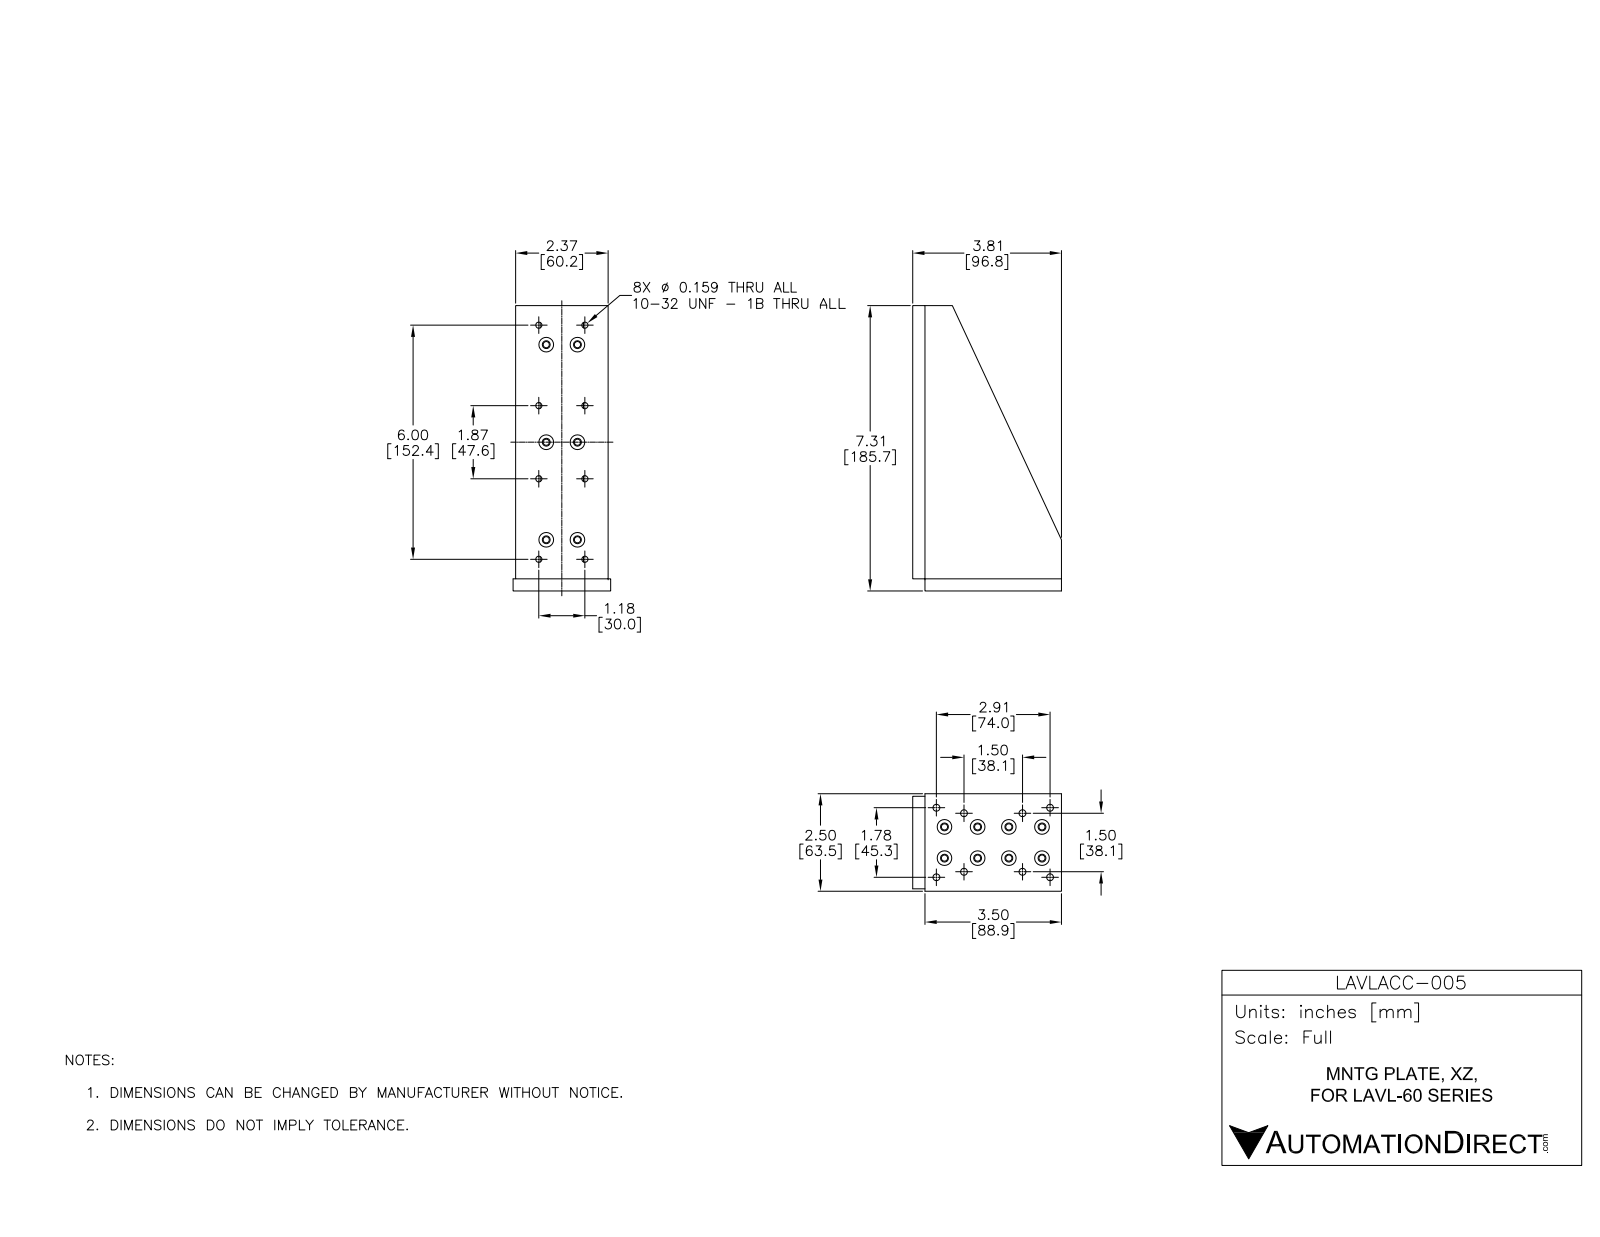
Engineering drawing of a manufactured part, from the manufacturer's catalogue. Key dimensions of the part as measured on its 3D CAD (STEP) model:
Part name (STEP PRODUCT): LAVLACC-005
STEP written by: SolidWorks 2015 (AUTOMOTIVE_DESIGN)
Units: inches
Bodies: 4 solids, 208 faces (48 planar, 132 cylindrical, 28 other)
Overall size (bounding box): 7.313 × 3.813 × 2.5
Volume: 17.28 in³ · Surface area: 146.8 in²
Round holes (diameter × count): ⌀0.159 ×22, ⌀0.201 ×14, ⌀0.375 ×14, ⌀0.177 ×4, ⌀0.177 ×4, ⌀0.313 ×4, ⌀0.315 ×4
Main face-to-face distances: 0.8, 0.312, 0.313, 1.112, 0.488, 0.63, 0.942, 1.43, 1.742, 2.371
Hole centre spacings: 0.8, 1.202, 2.5, 2.625, 0.495, 0.535, 0.61, 0.85
